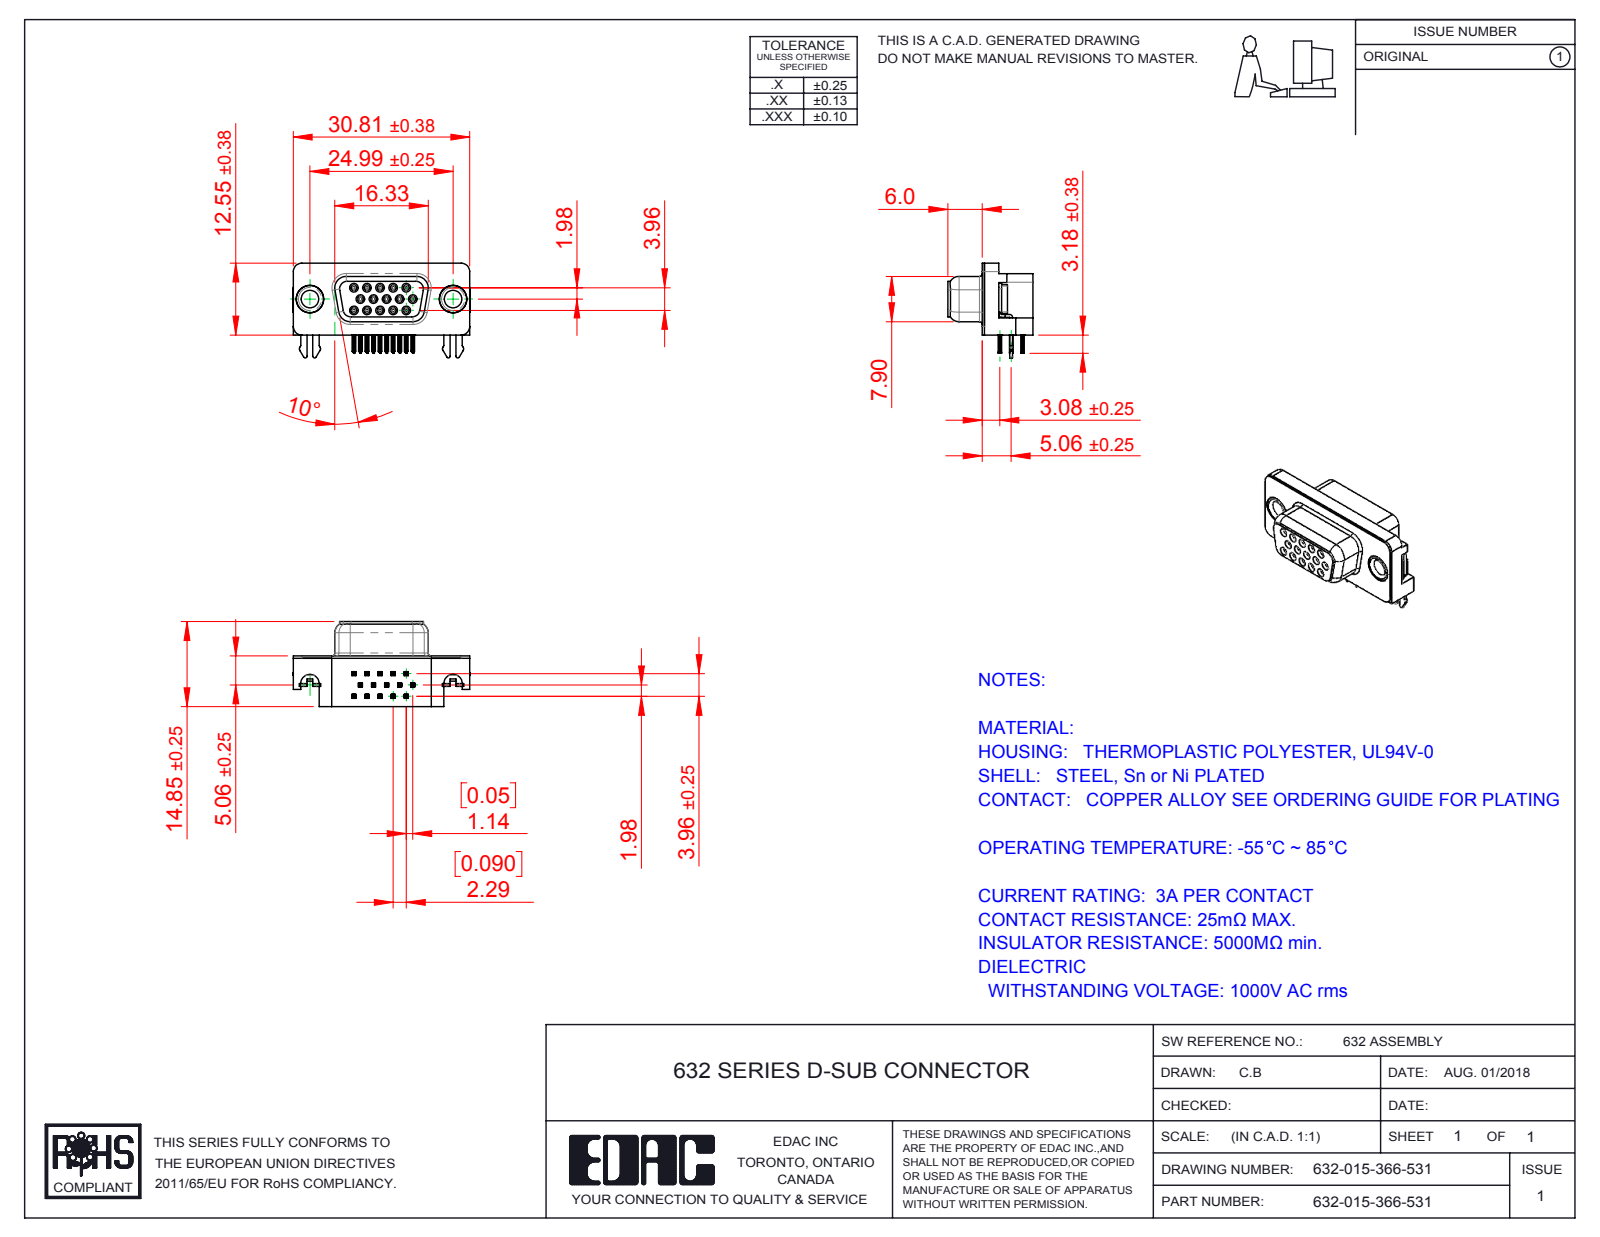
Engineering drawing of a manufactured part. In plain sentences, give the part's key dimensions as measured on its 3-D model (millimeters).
The part is named "632 Thru Hole Rivet; 632 Contact Top; 632-015-366-501; 632 Contact Middle (+4 more)". Its 3-D file was written by "SolidWorks 2016 (CONFIG_CONTROL_DESIGN)". It is 21 solids with 2298 faces: 990 planar, 594 cylindrical and 714 other. Overall it measures 30.89 by 16.55 by 14.85 millimeters. Its volume is 2 908 cubic millimeters and its surface area 4 994 square millimeters. Round holes: 15 of diameter 0.8, 15 of diameter 0.9, 2 of diameter 3.05, 2 of diameter 4, 2 of diameter 4.8, 2 of diameter 5. Round bosses or shafts: 15 of diameter 1.2, 2 of diameter 4.9, 2 of diameter 4.75, 2 of diameter 3.85. Partial cylindrical surfaces (rounded edges, fillets, slot ends): 120 of radius 0.1, 60 of radius 0.15, 30 of radius 0.35, 15 of radius 0.34, 11 of radius 1, 10 of radius 0.28, 10 of radius 0.5, 8 of radius 0.25. The main face-to-face distances are 0.4, 1.98, 8.45, 8.85, 2.9, 2.5, 5.95, 6.4, 6.7, 7.05. The hole center spacings are 2.28, 2.29, 3.96, 4.57, 6.05, 3.97, 4.58, 6.86.
